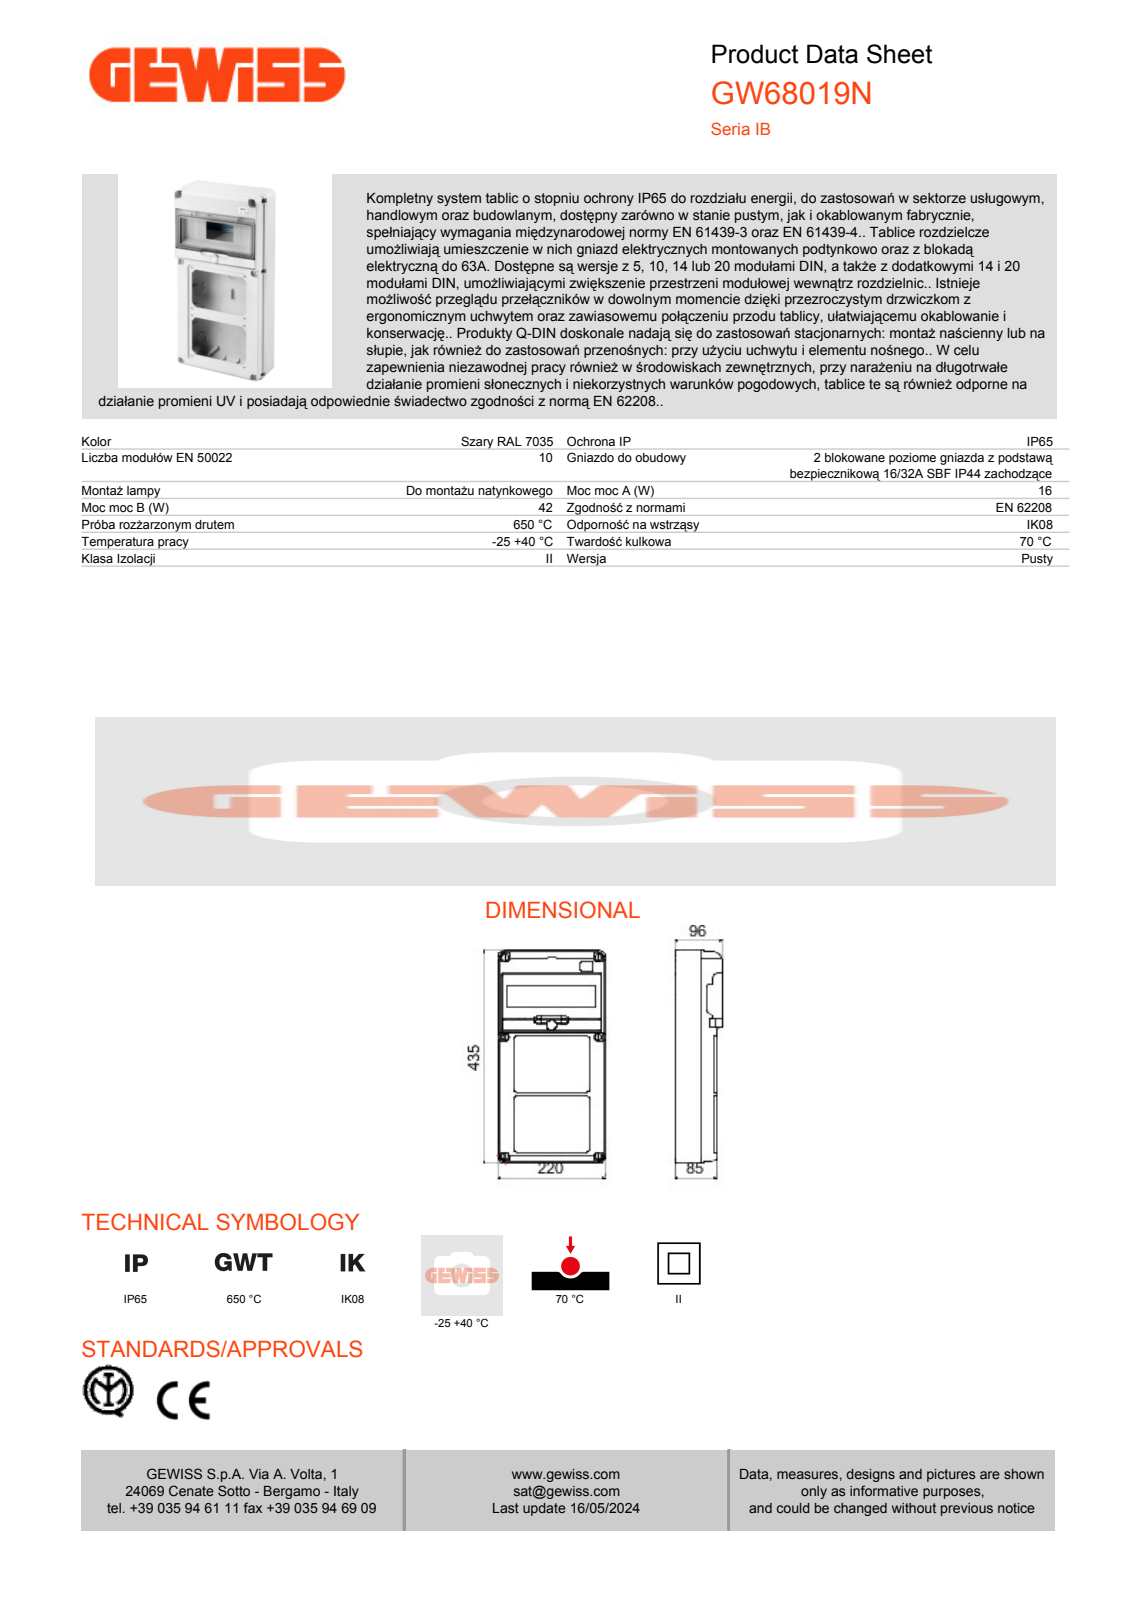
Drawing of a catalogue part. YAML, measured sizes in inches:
part_name: "5525059_FONDO_QDIN_10M; 55524011H_FRONTALE_QDIN_10M_2FL; GW68019N_1_ASM"
step_written_by: "CREO PARAMETRIC BY PTC INC, 2020354 (CONFIG_CONTROL_DESIGN)"
units: inches
bodies: {solids: 2, faces: 839, planar: 466, cylindrical: 109, other: 264}
overall_size: [17.126, 8.661, 3.983]
volume: 106.7
surface_area: 945.6
partial_cylinders:
  - {radius: 0.039, count: 16}
  - {radius: 0.079, count: 12}
  - {radius: 0.059, count: 7}
  - {radius: 0.075, count: 7}
  - {radius: 0.098, count: 7}
  - {radius: 0.118, count: 4}
  - {radius: 0.591, count: 4}
  - {radius: 0.177, count: 3}
face_to_face_distances: [0.118, 0.472, 3.74, 3.622, 0.087, 2.894, 8.374, 0.117, 1.213, 8.661]
